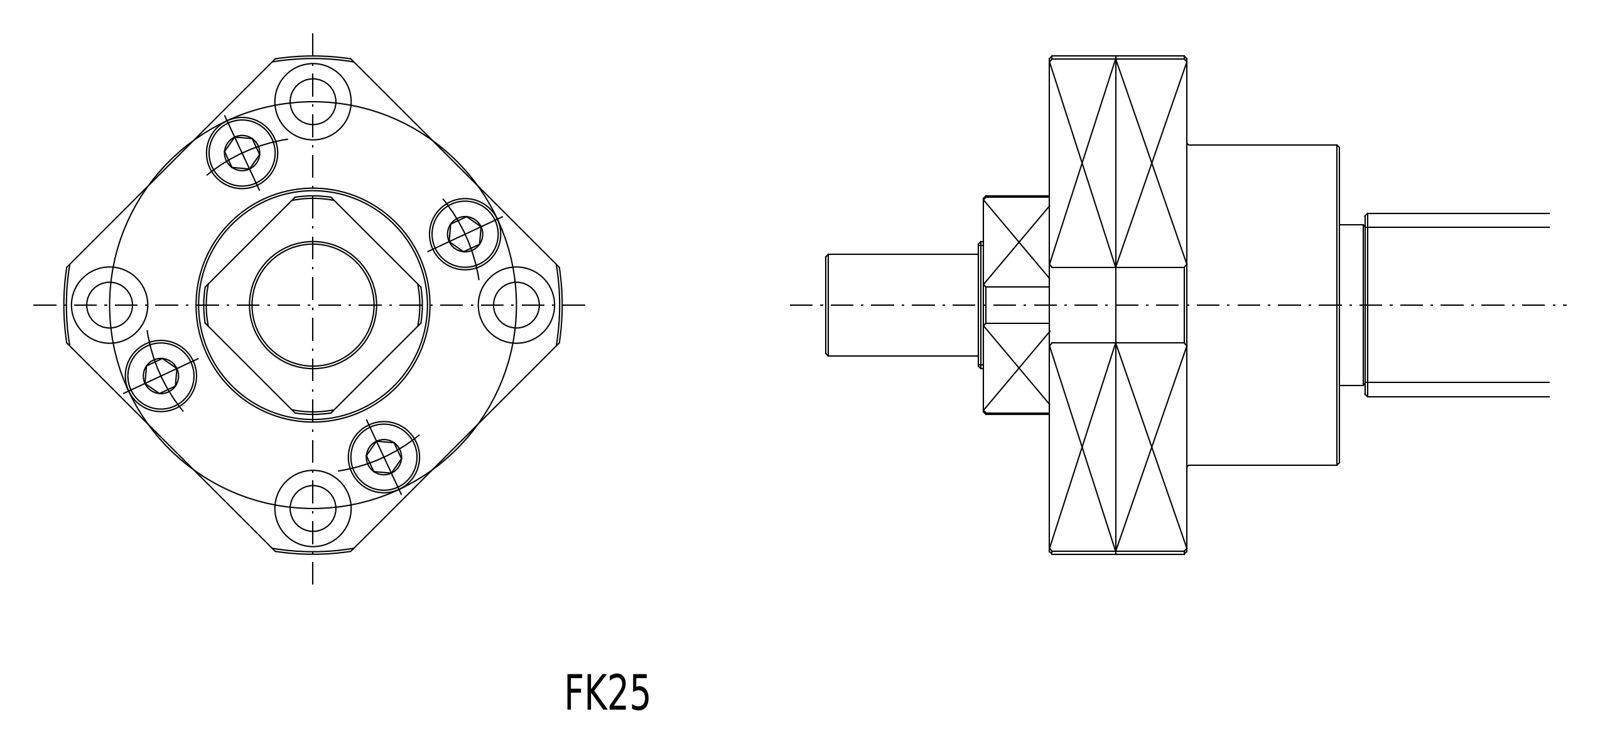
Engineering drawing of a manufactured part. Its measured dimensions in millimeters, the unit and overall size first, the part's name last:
Units: millimetres
Overall size (bounding box): 79 × 79 × 73
Round holes (diameter × count): ⌀14 ×8, ⌀6.8 ×4, ⌀8.6 ×4, ⌀9 ×4, ⌀5 ×2, ⌀23.5 ×1, ⌀25 ×1, ⌀34 ×1, ⌀42 ×1, ⌀45 ×1, ⌀46.5 ×1
Round bosses / shafts (diameter × count): ⌀63 ×1, ⌀62.4 ×1, ⌀52 ×1, ⌀43 ×1, ⌀36 ×1, ⌀35 ×1, ⌀32.2 ×1, ⌀32 ×1
Partial cylindrical surfaces — rounded edges, fillets, slot ends (radius × count): R49 ×1
Main face-to-face distances: 14, 10, 13, 15, 30, 79, 44, 27, 25, 34
Hole centre spacings: 17.21, 33, 39.66, 39.99, 46.67, 56.56, 61.68, 71.28
Volume: 185 014 mm³ · Surface area: 88 517 mm²
Bodies: 39 solids, 469 faces (70 planar, 143 cylindrical, 256 other)
Part name (STEP PRODUCT): FK25組合件
STEP written by: SolidWorks 2008 (CONFIG_CONTROL_DESIGN)
